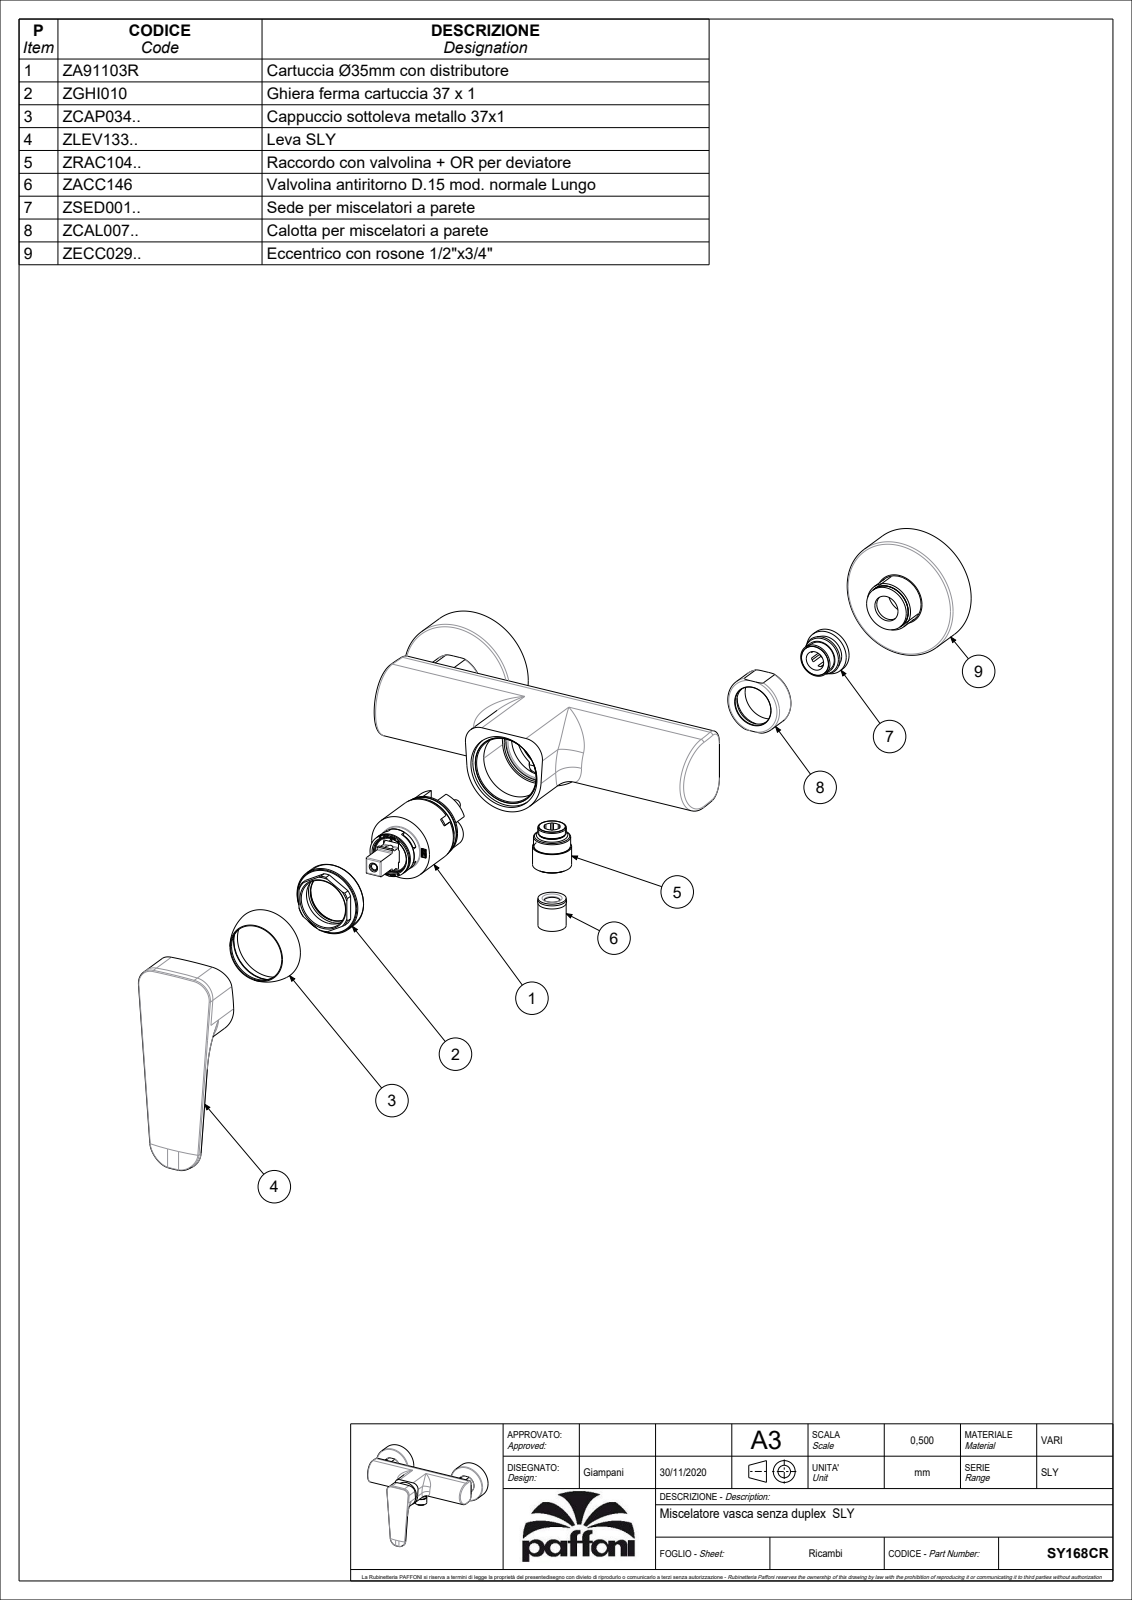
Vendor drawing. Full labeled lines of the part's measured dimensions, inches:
Part name (STEP PRODUCT): SY168CR
STEP written by: CREO PARAMETRIC BY PTC INC, 2020044 (CONFIG_CONTROL_DESIGN)
Units: inches
Bodies: 1 solid, 1422 faces (734 planar, 394 cylindrical, 294 other)
Overall size (bounding box): 8.406 × 5.209 × 4.892
Volume: 11.68 in³ · Surface area: 216.5 in²
Round holes (diameter × count): ⌀0.354 ×3, ⌀0.472 ×3, ⌀0.13 ×2, ⌀0.157 ×2, ⌀0.315 ×2, ⌀0.413 ×2, ⌀0.709 ×2, ⌀0.85 ×2, ⌀0.965 ×2, ⌀0.984 ×2, ⌀2.453 ×2, ⌀0.118 ×1
Round bosses / shafts (diameter × count): ⌀2.5 ×2, ⌀1.063 ×2, ⌀0.945 ×2, ⌀0.697 ×2, ⌀0.315 ×2, ⌀1.378 ×1, ⌀1.37 ×1, ⌀1.331 ×1
Partial cylindrical surfaces — rounded edges, fillets, slot ends (radius × count): R0.02 ×44, R0.006 ×11, R0.012 ×9, R0.394 ×8, R0.059 ×6, R0.039 ×4, R0.256 ×4, R0.276 ×4
Main face-to-face distances: 0.138, 0.024, 0.728, 0.591, 1.437, 0.752, 0.118, 0.614, 0.02, 0.413
Hole centre spacings: 0.028, 0.335, 0.339, 0.513, 0.52, 0.532, 2.693, 2.715
